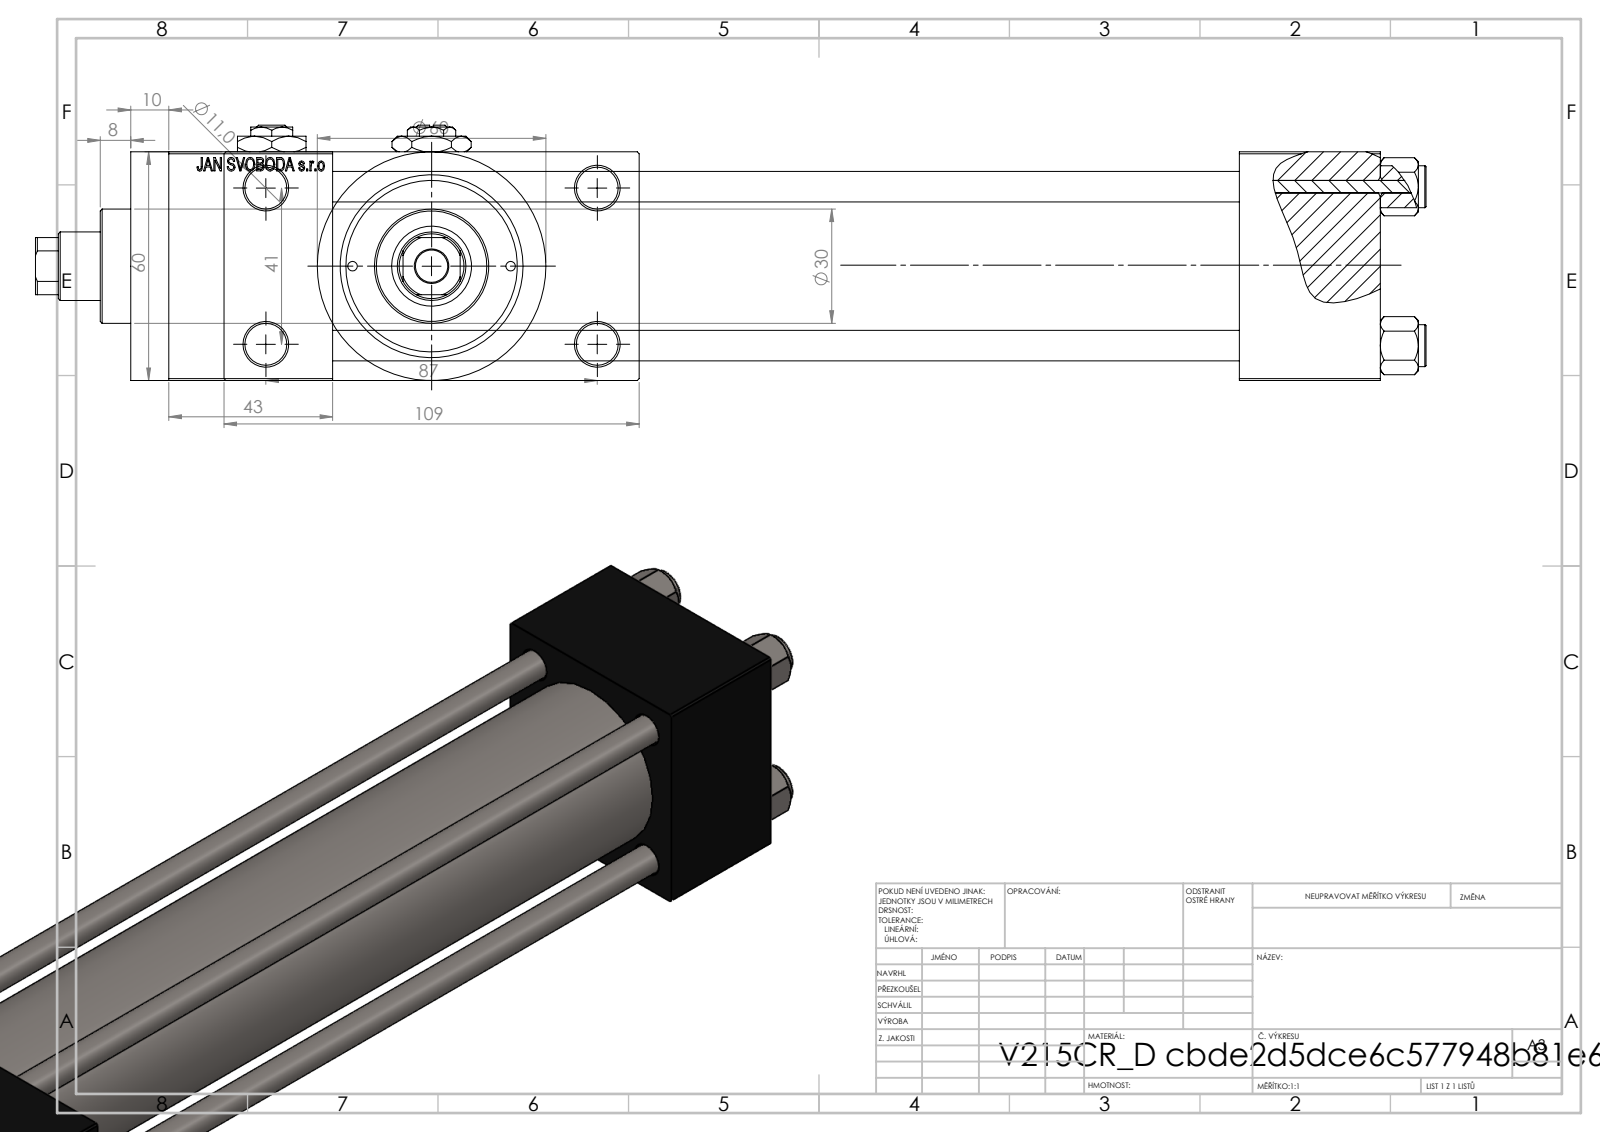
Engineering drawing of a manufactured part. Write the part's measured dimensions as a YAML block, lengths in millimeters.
part_name: "V215CR_VCP_D; Zatka_pro_OIL_PORT; NUT_M5_D; V215CR_D_TYCINKA (+2 more)"
step_written_by: "SolidWorks 2019 (CONFIG_CONTROL_DESIGN)"
units: millimeters
bodies: {solids: 12, faces: 1160, planar: 524, cylindrical: 96, other: 540}
overall_size: [365, 109, 67]
volume: 666820
surface_area: 200321
round_holes:
  - {diameter: 8, count: 4}
  - {diameter: 11, count: 4}
  - {diameter: 16.66, count: 3}
  - {diameter: 24, count: 3}
  - {diameter: 2.5, count: 2}
  - {diameter: 7, count: 2}
  - {diameter: 8.5, count: 1}
  - {diameter: 18, count: 1}
  - {diameter: 21, count: 1}
  - {diameter: 31, count: 1}
  - {diameter: 40, count: 1}
  - {diameter: 45, count: 1}
round_bosses_or_shafts:
  - {diameter: 11, count: 4}
  - {diameter: 60, count: 1}
  - {diameter: 46, count: 1}
  - {diameter: 30, count: 1}
partial_cylinders:
  - {radius: 8.5, count: 1}
face_to_face_distances: [60, 238, 24.5, 84.5, 37, 275, 43, 318, 281, 10]
hole_center_spacings: [20.85, 22.65, 29.49, 30.62, 41.7, 46.53, 47.15, 48.09]
